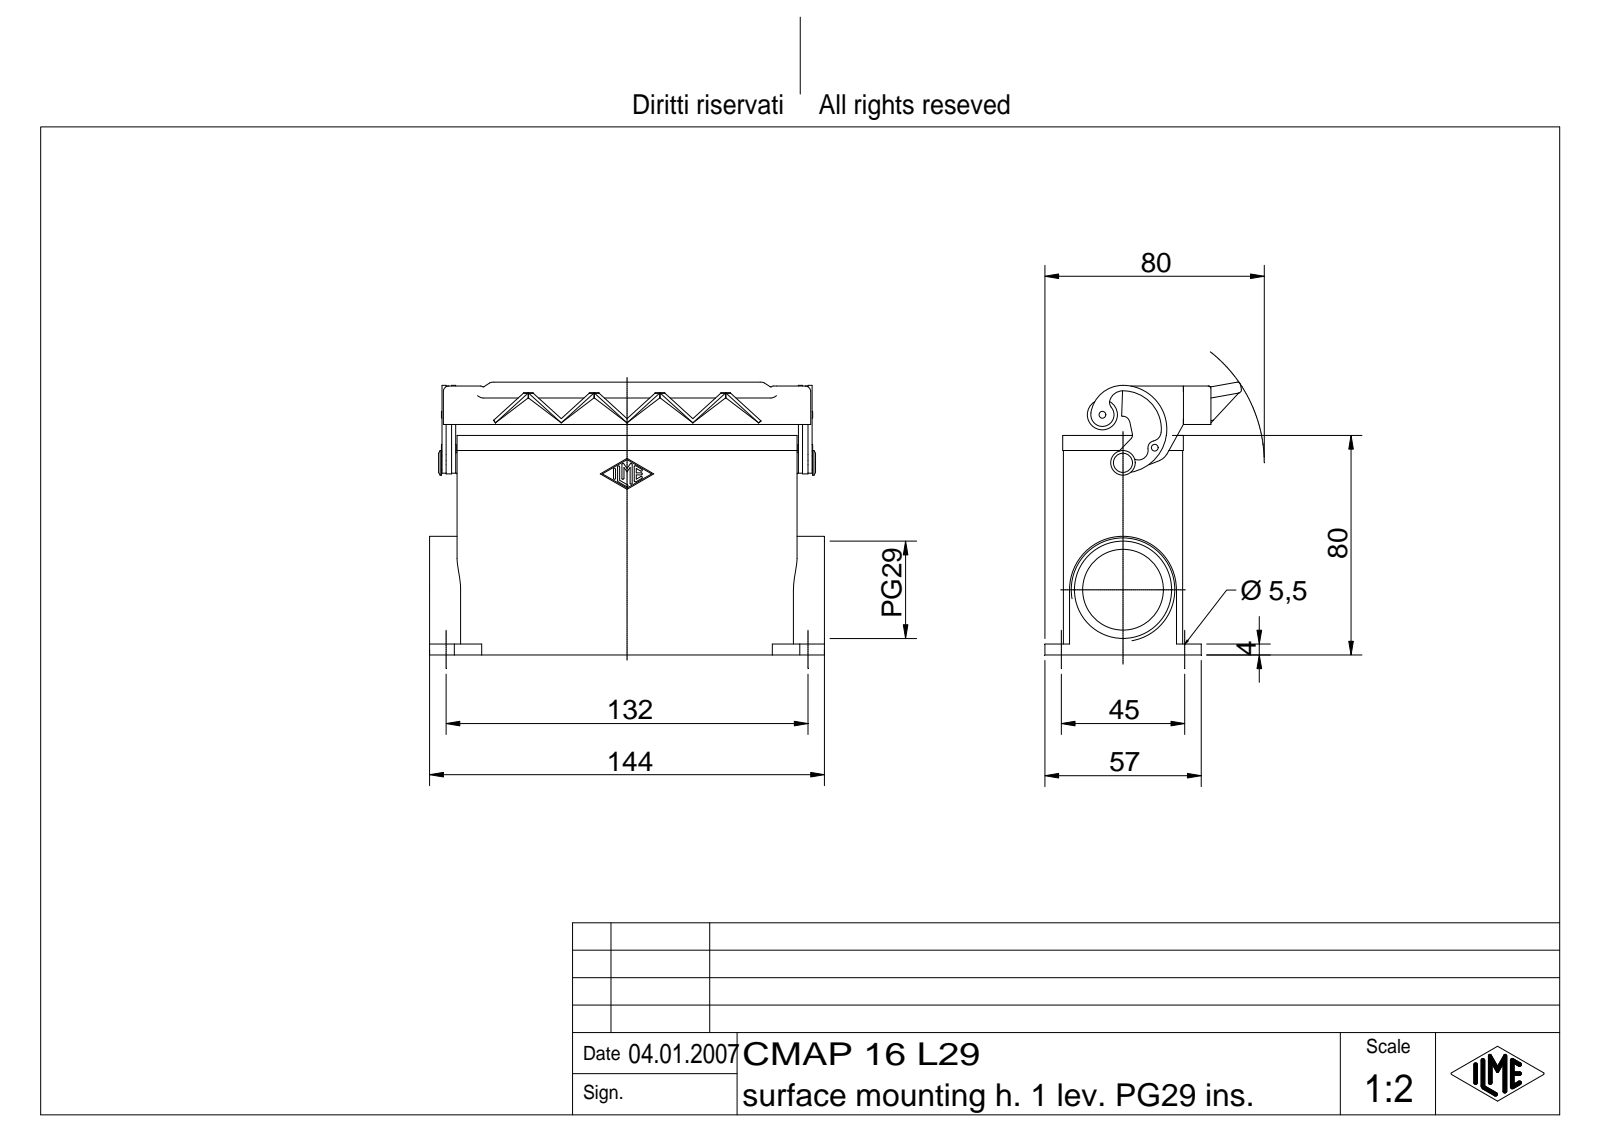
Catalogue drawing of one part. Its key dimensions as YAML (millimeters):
part_name: "CMAP 16 L29"
step_written_by: "Autodesk Inventor 7 (AUTOMOTIVE_DESIGN)"
units: millimeters
bodies: {solids: 4, faces: 466, planar: 194, cylindrical: 123, other: 149}
overall_size: [144, 99.42, 71.7]
volume: 150420
surface_area: 83919
round_holes:
  - {diameter: 5.5, count: 4}
  - {diameter: 2, count: 1}
  - {diameter: 29.48, count: 1}
  - {diameter: 35.48, count: 1}
round_bosses_or_shafts:
  - {diameter: 11, count: 1}
  - {diameter: 9, count: 1}
  - {diameter: 5, count: 1}
  - {diameter: 3, count: 1}
  - {diameter: 2.5, count: 1}
partial_cylinders:
  - {radius: 0.38, count: 14}
  - {radius: 2, count: 12}
  - {radius: 6, count: 8}
  - {radius: 1, count: 7}
  - {radius: 1.5, count: 5}
  - {radius: 3, count: 4}
  - {radius: 2.5, count: 3}
  - {radius: 3.5, count: 2}
face_to_face_distances: [3, 40.5, 43.5, 4, 37.5, 3.25, 0.75, 10.5, 74.5, 70.5]
hole_center_spacings: [45, 132, 139.46, 53.04]
